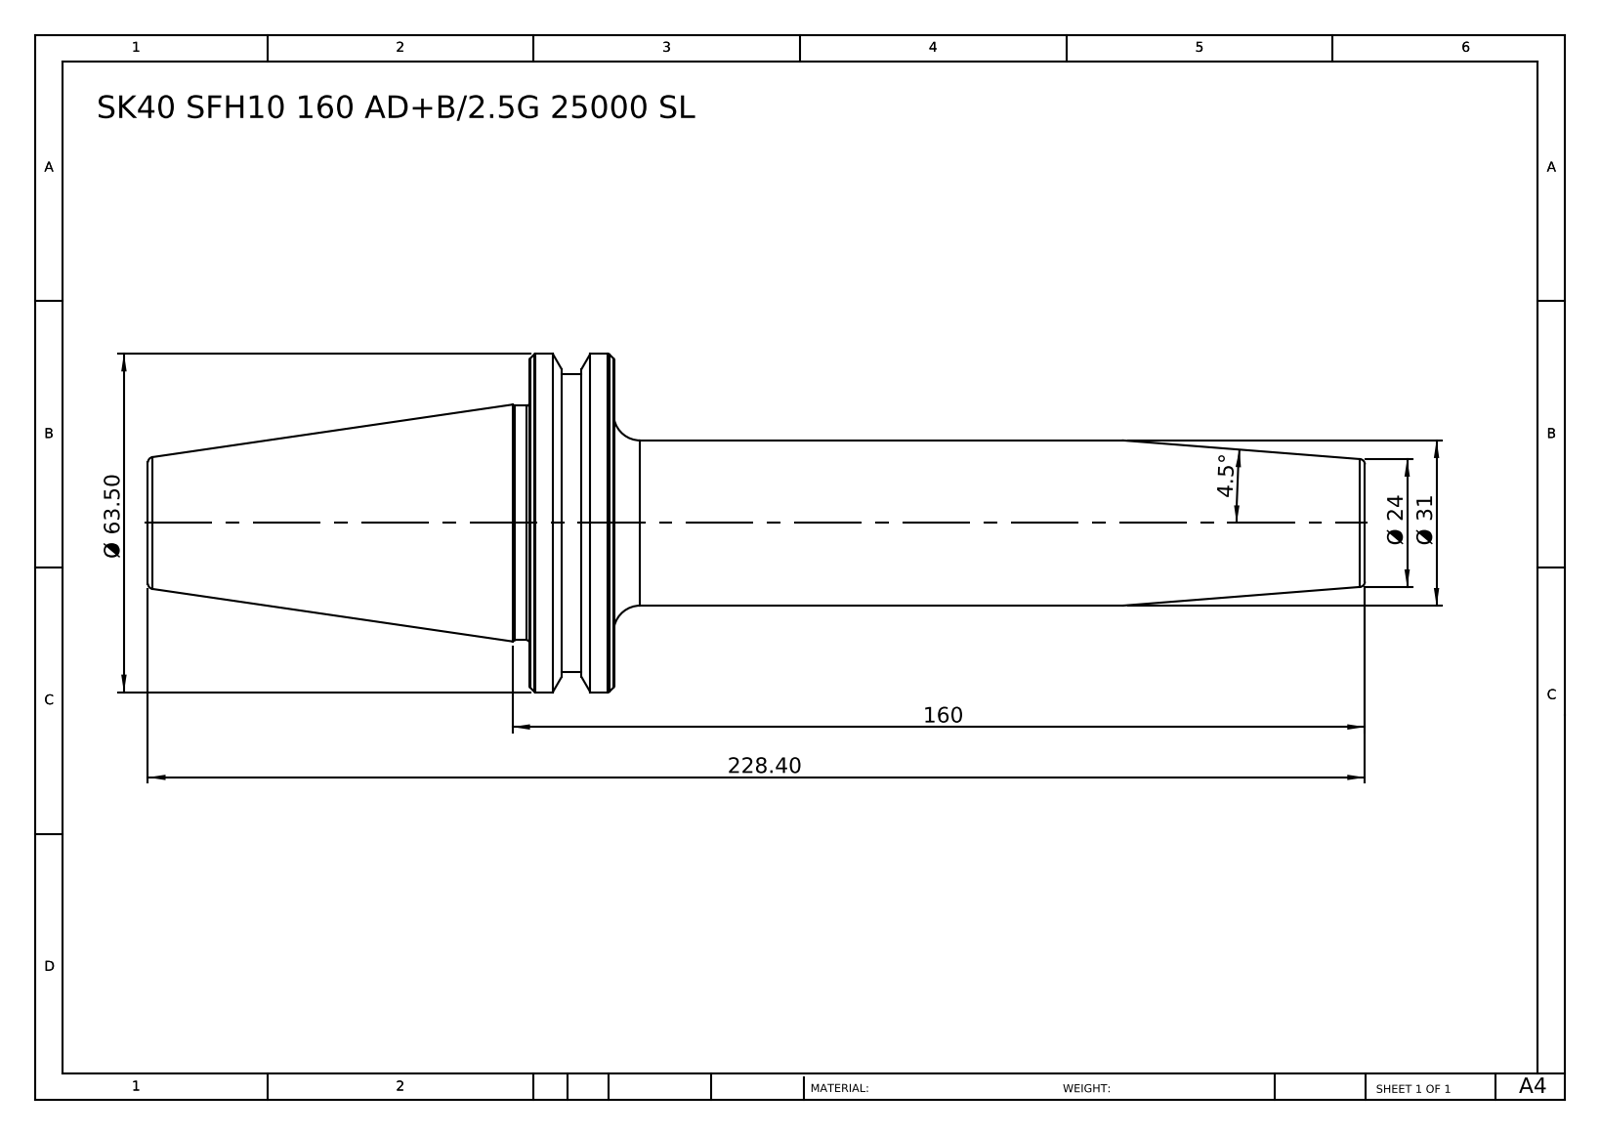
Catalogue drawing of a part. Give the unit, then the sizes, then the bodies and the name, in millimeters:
Units: millimetres
Overall size (bounding box): 228.4 × 63.5 × 63.5
Round bosses / shafts (diameter × count): ⌀63.5 ×1, ⌀56 ×1, ⌀44 ×1, ⌀31 ×1
Main face-to-face distances: 15.9, 87.5, 71.6, 140.9, 156.8, 228.4, 147, 6.1, 9.8, 81.4
Volume: 216 208 mm³ · Surface area: 29 744 mm²
Bodies: 1 solid, 46 faces (6 planar, 10 cylindrical, 30 other)
Part name (STEP PRODUCT): SK40 SFH10 160 AD+B-2.5G 25000 SL
STEP written by: SolidWorks 2014 (CONFIG_CONTROL_DESIGN)
